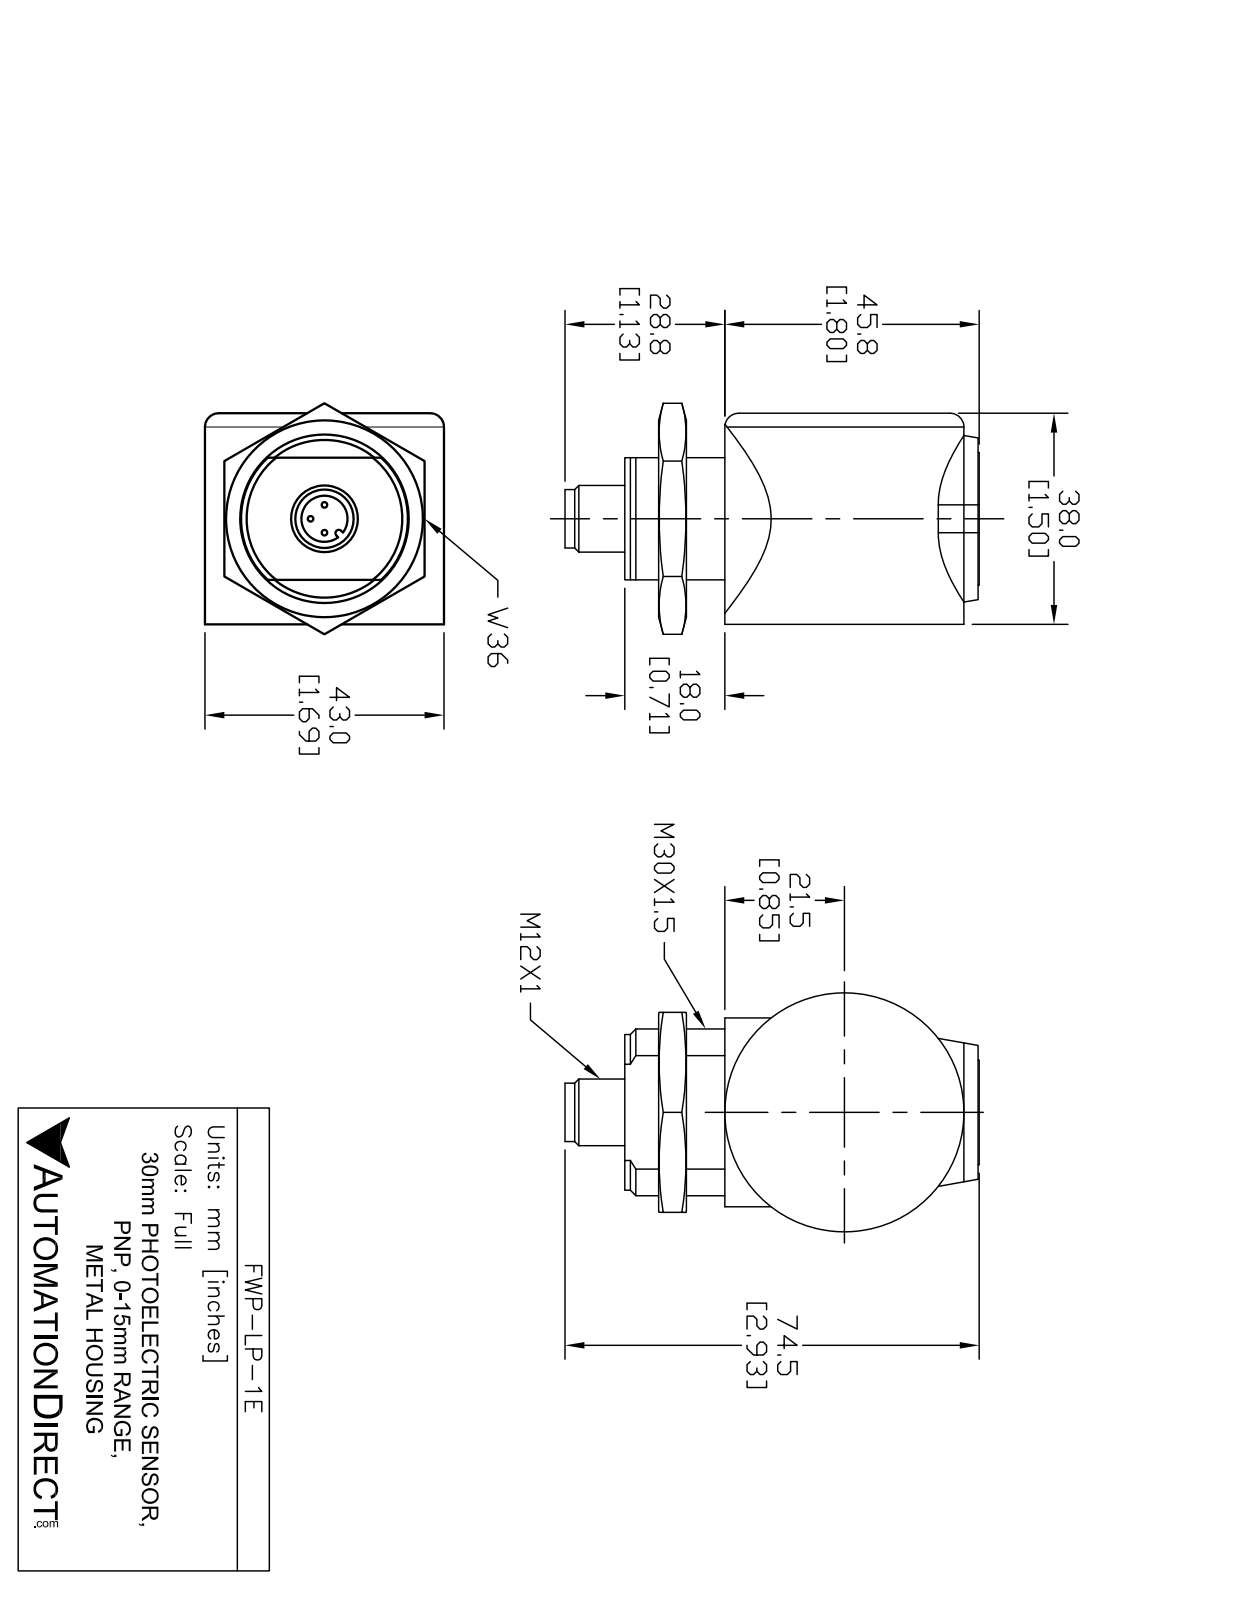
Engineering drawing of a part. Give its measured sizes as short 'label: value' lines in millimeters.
name: FWP-LP-1E
written by: SolidWorks 2013 (AUTOMOTIVE_DESIGN)
unit: mm
bodies: 1 solid, 60 faces (29 planar, 24 cylindrical, 7 other)
size: 74.4 × 42.9 × 37.8
volume: 72 380 mm³; area: 12 480 mm²
holes: 1× ⌀8
bosses: 3× ⌀1, 1× ⌀42.9, 1× ⌀11.9, 1× ⌀9.9
rounds: 2× R16.3, 1× R0.6, 1× R13.8, 1× R14.9
face distances: 37.8, 64, 2.8, 61.2, 7.6, 4.8, 56.3, 29.9, 7.9, 7.9
